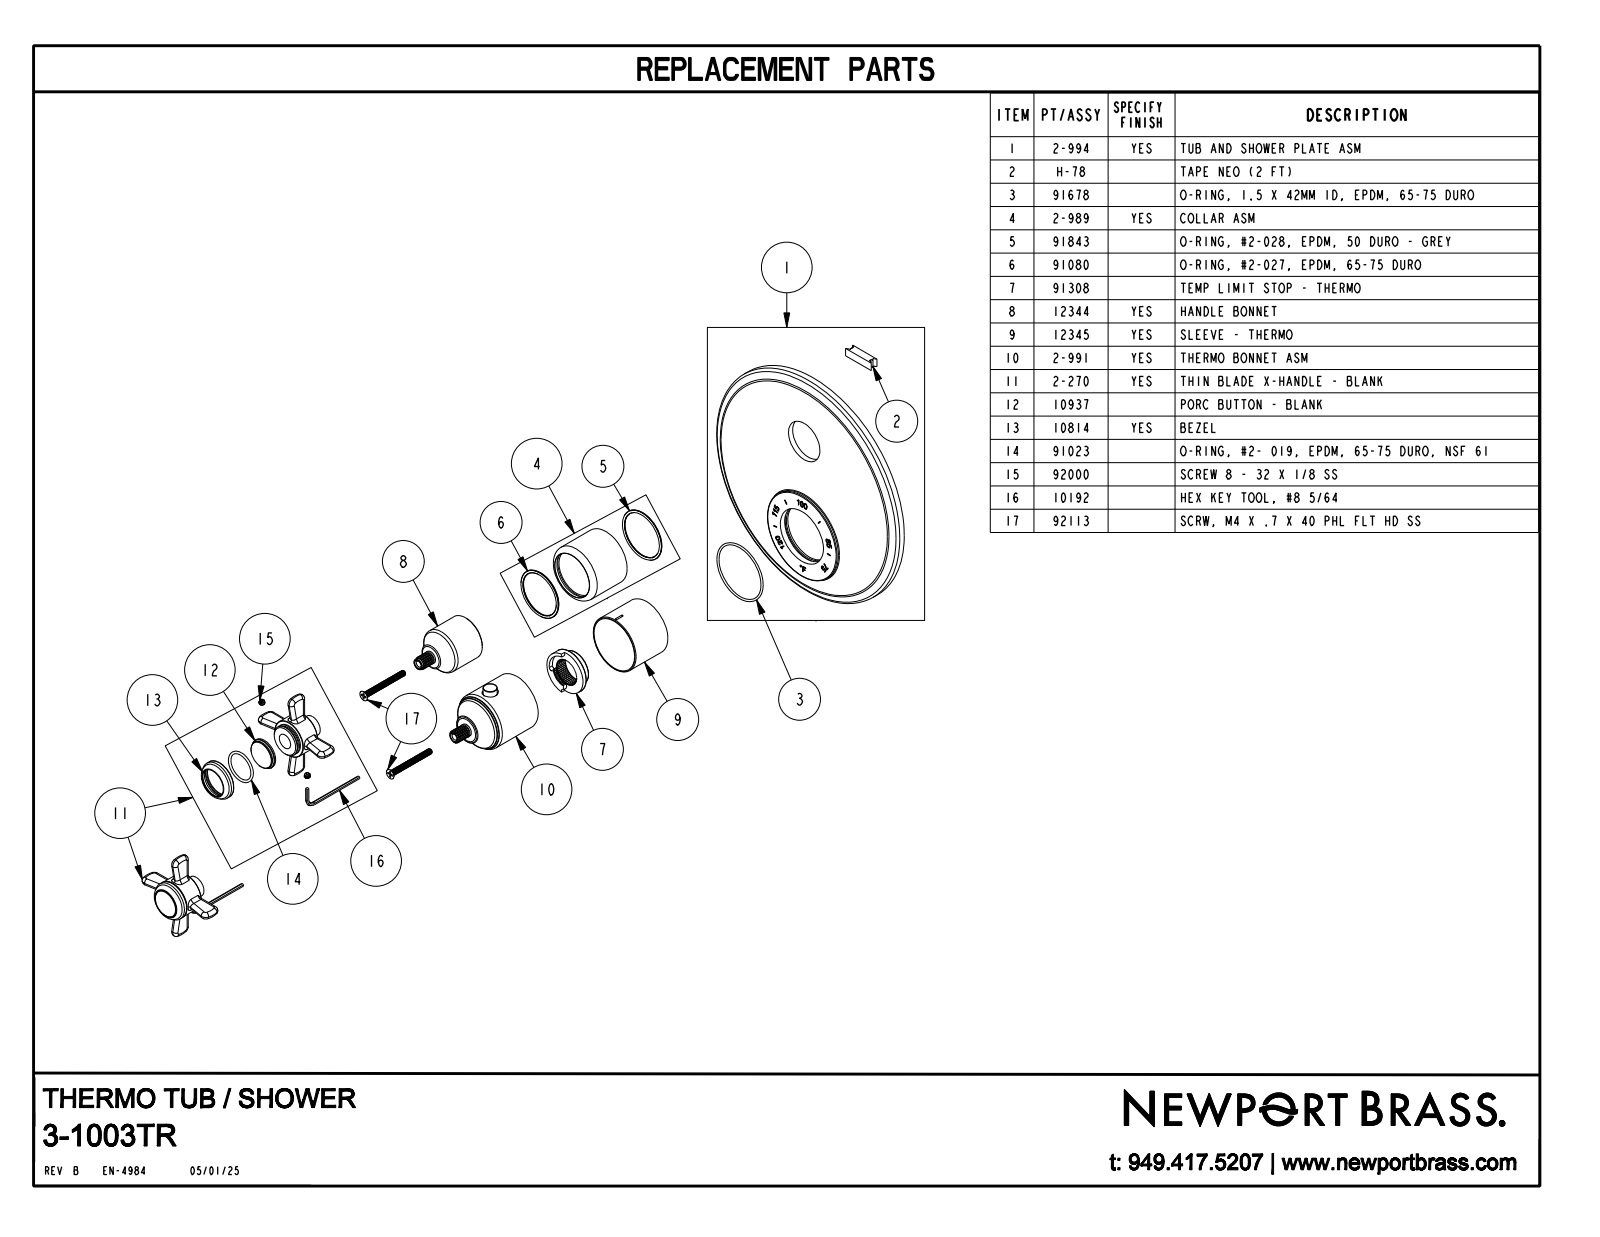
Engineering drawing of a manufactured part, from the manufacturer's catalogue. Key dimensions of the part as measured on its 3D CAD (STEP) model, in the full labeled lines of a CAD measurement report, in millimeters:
Part name (STEP PRODUCT): 12346_AF5; H-78_2_FEET_AF15; 91678; 2-994_AF5_ASM (+8 more)
STEP written by: PRO/ENGINEER BY PARAMETRIC TECHNOLOGY CORPORATION, 2013150 (CONFIG_CONTROL_DESIGN)
Units: millimetres
Bodies: 28 solids, 3071 faces (885 planar, 720 cylindrical, 1466 other)
Overall size (bounding box): 180 × 180 × 117.2
Volume: 169 900 mm³ · Surface area: 184 800 mm²
Round holes (diameter × count): ⌀3.3 ×4, ⌀4.8 ×2, ⌀11.1 ×2, ⌀20.7 ×2, ⌀1.4 ×1, ⌀2 ×1, ⌀2.5 ×1, ⌀3.2 ×1, ⌀7 ×1, ⌀7 ×1, ⌀10.3 ×1, ⌀25.8 ×1
Round bosses / shafts (diameter × count): ⌀4.2 ×4, ⌀4 ×3, ⌀42 ×2, ⌀28.3 ×2, ⌀27.9 ×2, ⌀22.6 ×2, ⌀22.2 ×2, ⌀20.4 ×2
Partial cylindrical surfaces — rounded edges, fillets, slot ends (radius × count): R2.5 ×20, R1.2 ×3, R4.3 ×3, R4.3 ×3, R1 ×2, R1.9 ×2, R2.1 ×2, R4.2 ×2
Main face-to-face distances: 2, 2.1, 4.1, 4.3, 2.3, 6.4, 9.3, 5.1, 4.7, 6.8
Hole centre spacings: 9.3, 14.1, 20.3, 25.9, 26, 29.6, 39.9, 40
